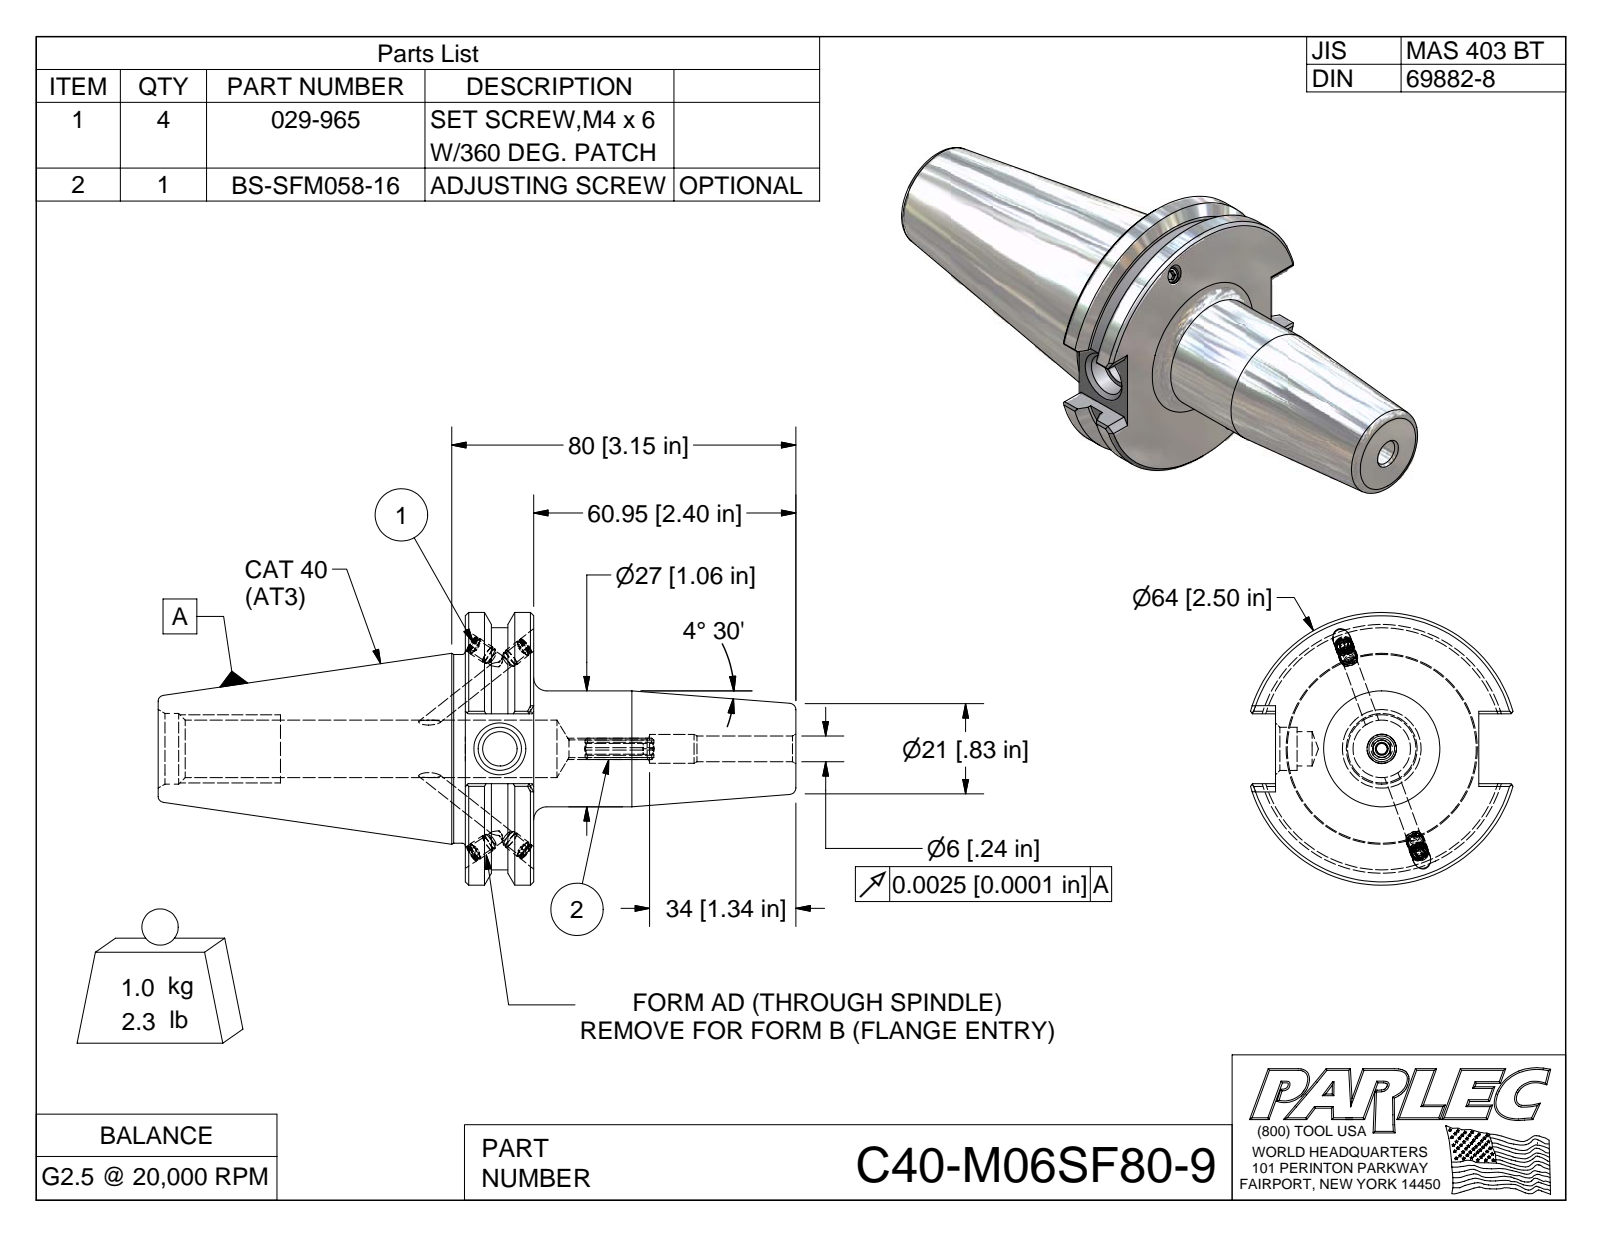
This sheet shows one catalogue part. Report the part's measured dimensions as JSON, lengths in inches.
{"part_name": "C40-M06SF80-9; C40BC-M06SF80-9-1; 029-965; BS-SFM058-16", "step_written_by": "Autodesk Inventor 2009 (AUTOMOTIVE_DESIGN)", "units": "inches", "bodies": {"solids": 6, "faces": 172, "planar": 87, "cylindrical": 32, "other": 53}, "overall_size": [5.837, 2.5, 2.403], "volume_in3": 7.835, "surface_area_in2": 42.87, "round_holes": [[0.13, 4], [0.161, 4], [0.236, 1], [0.266, 1]], "round_bosses_or_shafts": [[0.165, 4], [0.157, 4], [2.5, 1], [2.219, 1], [1.73, 1], [1.063, 1]], "partial_cylinders_radius": [[0.098, 1]], "face_to_face_distances": [0.625, 3.025, 2.4, 0.64, 1.86, 2.812, 3.437, 5.837, 3.201, 0.389]}
